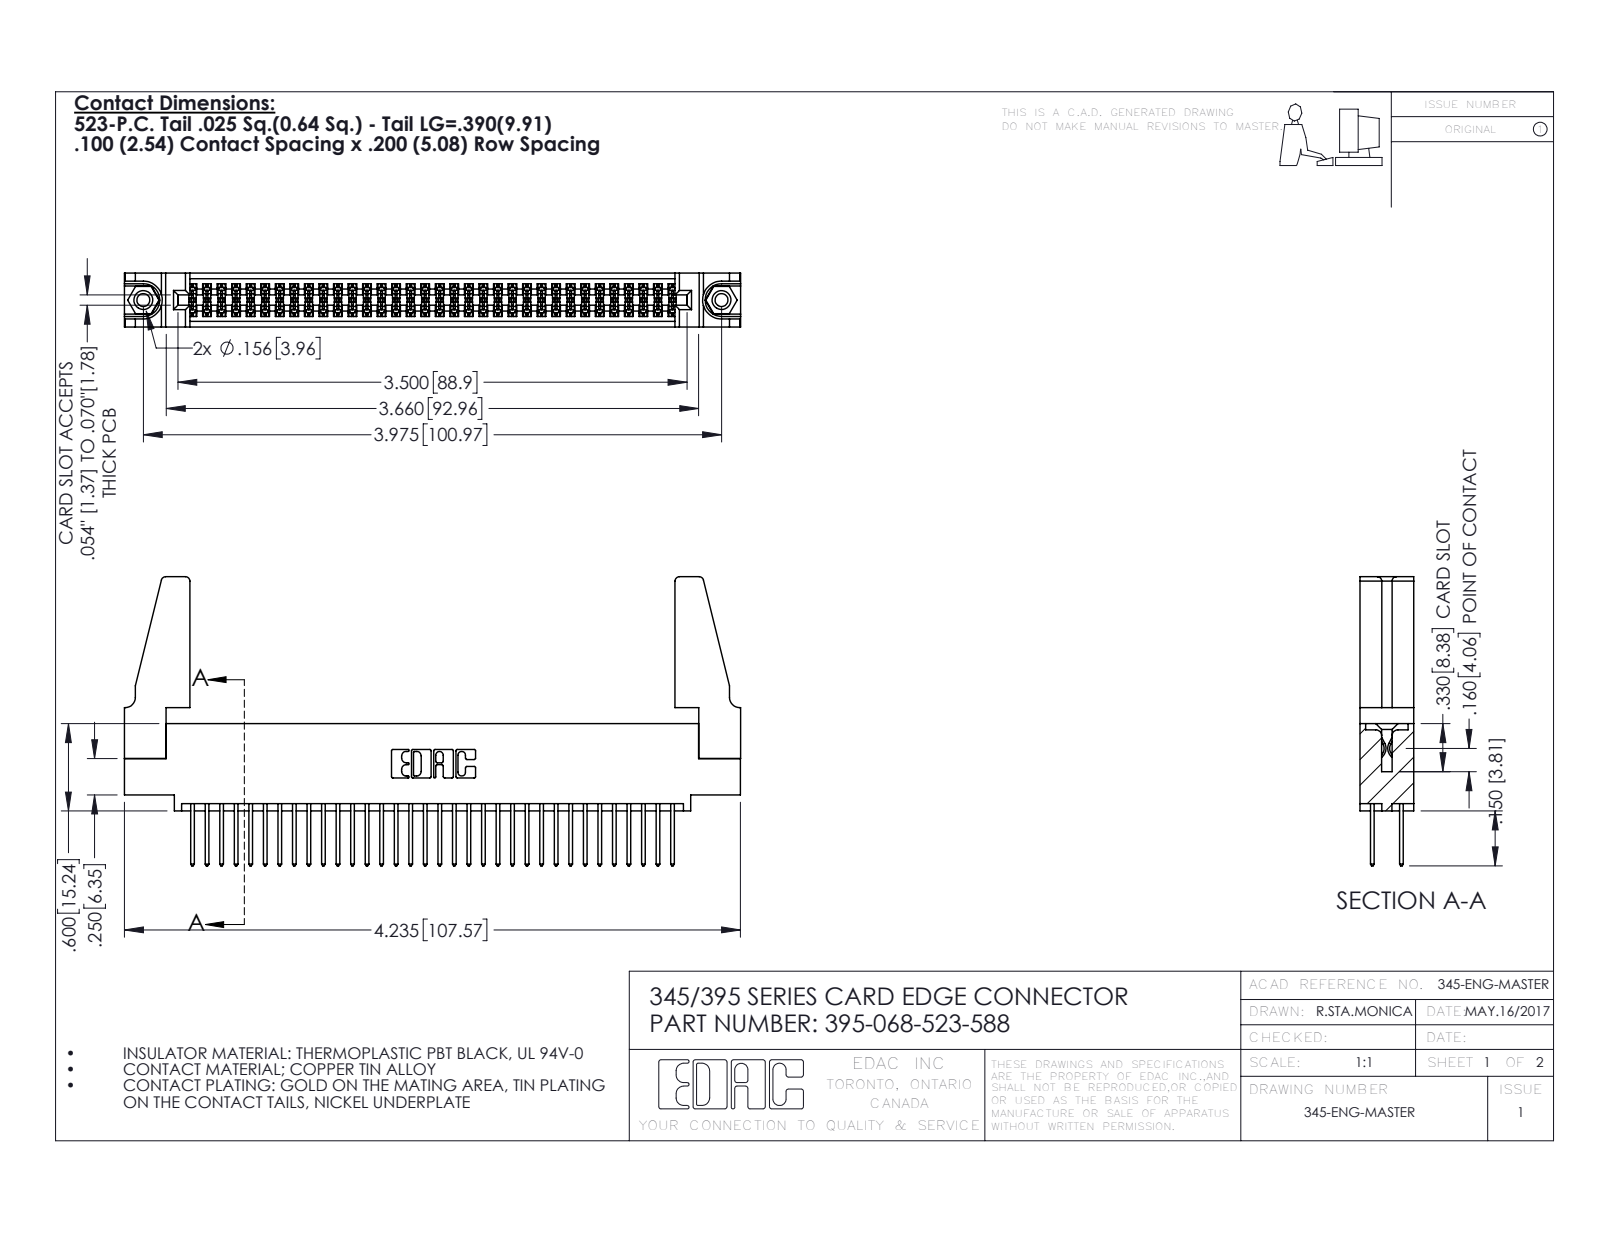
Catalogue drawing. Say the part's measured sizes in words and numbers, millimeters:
The part is named "345 Part_0.110 Offset - 0.156 Dia-TH; 345-220-078_345-220-088; 345-250-001_345-250-001-102; 395-068-523-588 (+1 more)". Its 3-D file was written by "SolidWorks 2016 (CONFIG_CONTROL_DESIGN)". It is 73 solids with 3654 faces: 2400 planar, 1238 cylindrical and 16 other. Overall it measures 107.6 by 50.5 by 9.4 millimeters. Its volume is 13 700 cubic millimeters and its surface area 19 120 square millimeters. Round holes: 2 of diameter 2.3, 2 of diameter 3.2, 2 of diameter 4, 1 of diameter 1.6. Round bosses or shafts: 2 of diameter 3.9. Partial cylindrical surfaces (rounded edges, fillets, slot ends): 102 of radius 0.2, 68 of radius 0.3, 22 of radius 0.3, 8 of radius 0.8, 6 of radius 0.2, 6 of radius 0.8, 3 of radius 0.7, 2 of radius 0.4. The main face-to-face distances are 1.8, 7.6, 9.4, 5.1, 2.5, 6.9, 0.6, 5.7, 4.4, 3.8. The hole center spacings are 6.9, 95, 101.
